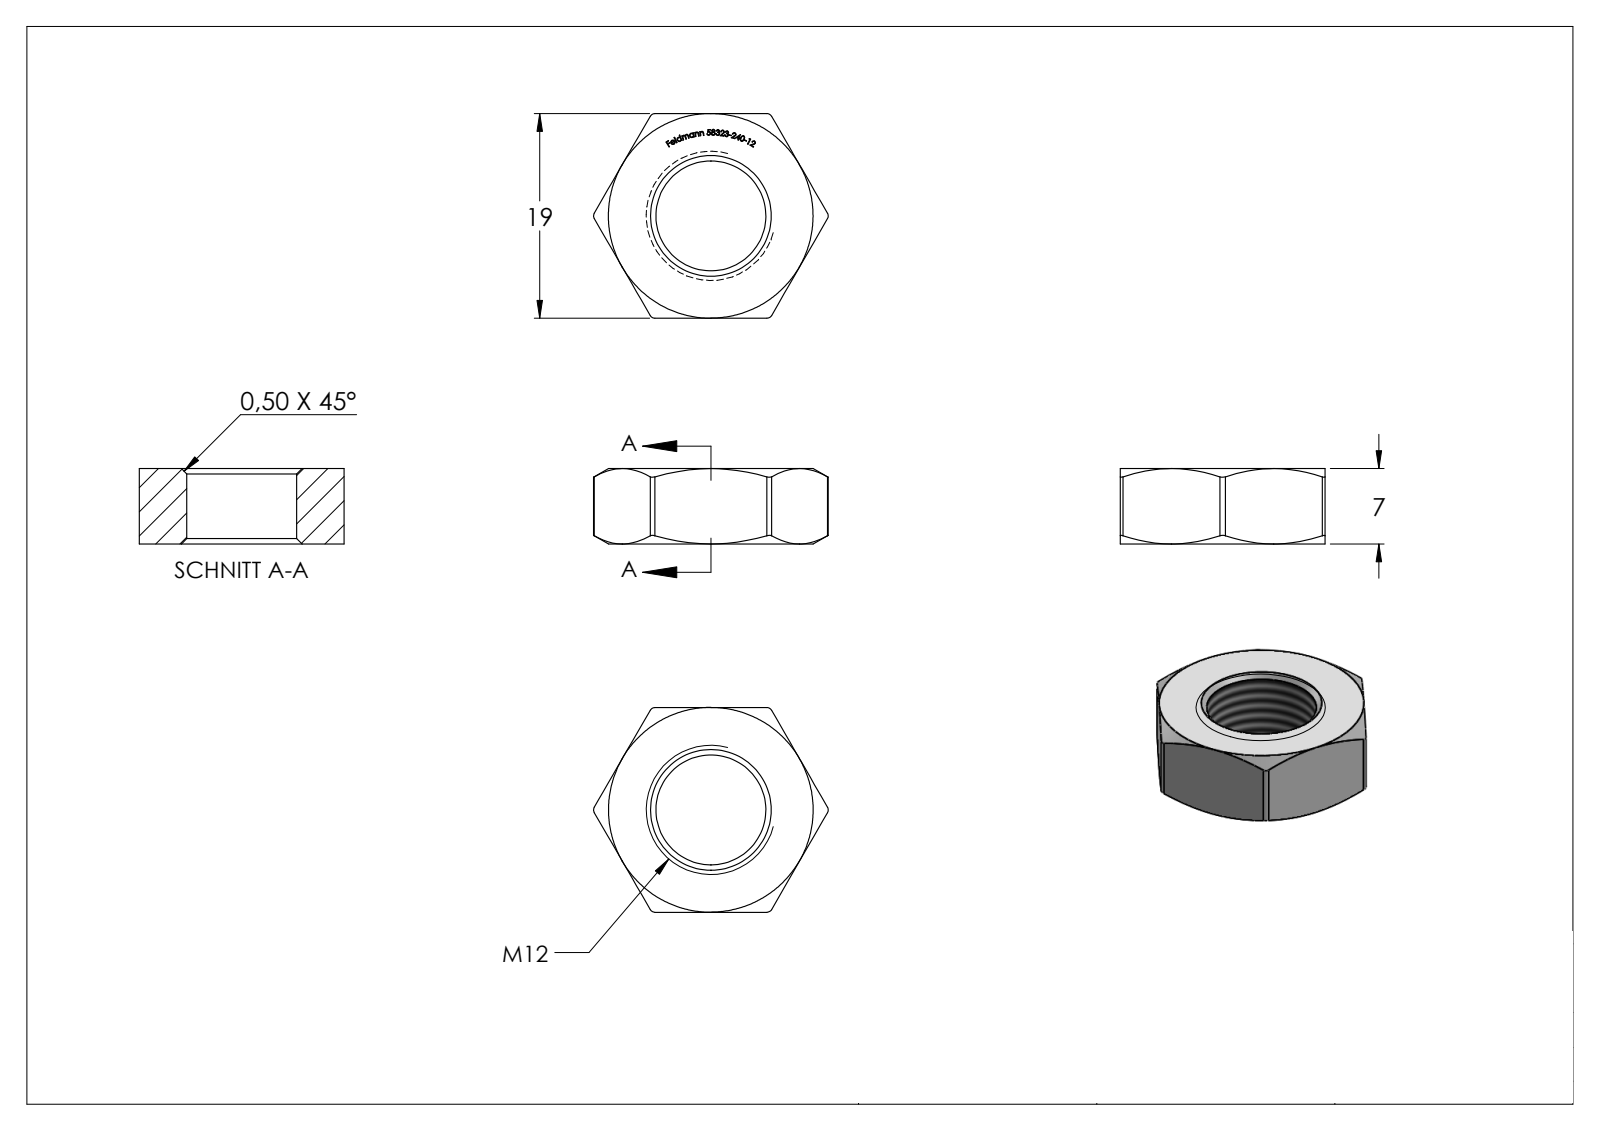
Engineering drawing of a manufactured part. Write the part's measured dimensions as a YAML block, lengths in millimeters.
part_name: "58323-240-12"
step_written_by: "SolidWorks 2015 (CONFIG_CONTROL_DESIGN)"
units: millimeters
bodies: {solids: 1, faces: 295, planar: 146, cylindrical: 7, other: 142}
overall_size: [22, 21.79, 19]
volume: 1593
surface_area: 1102
round_holes:
  - {diameter: 10.2, count: 1}
partial_cylinders:
  - {radius: 0.5, count: 6}
face_to_face_distances: [19, 7, 6.9, 0.53, 0.34, 0.31, 0.48, 0.58, 0.32, 0.39]
